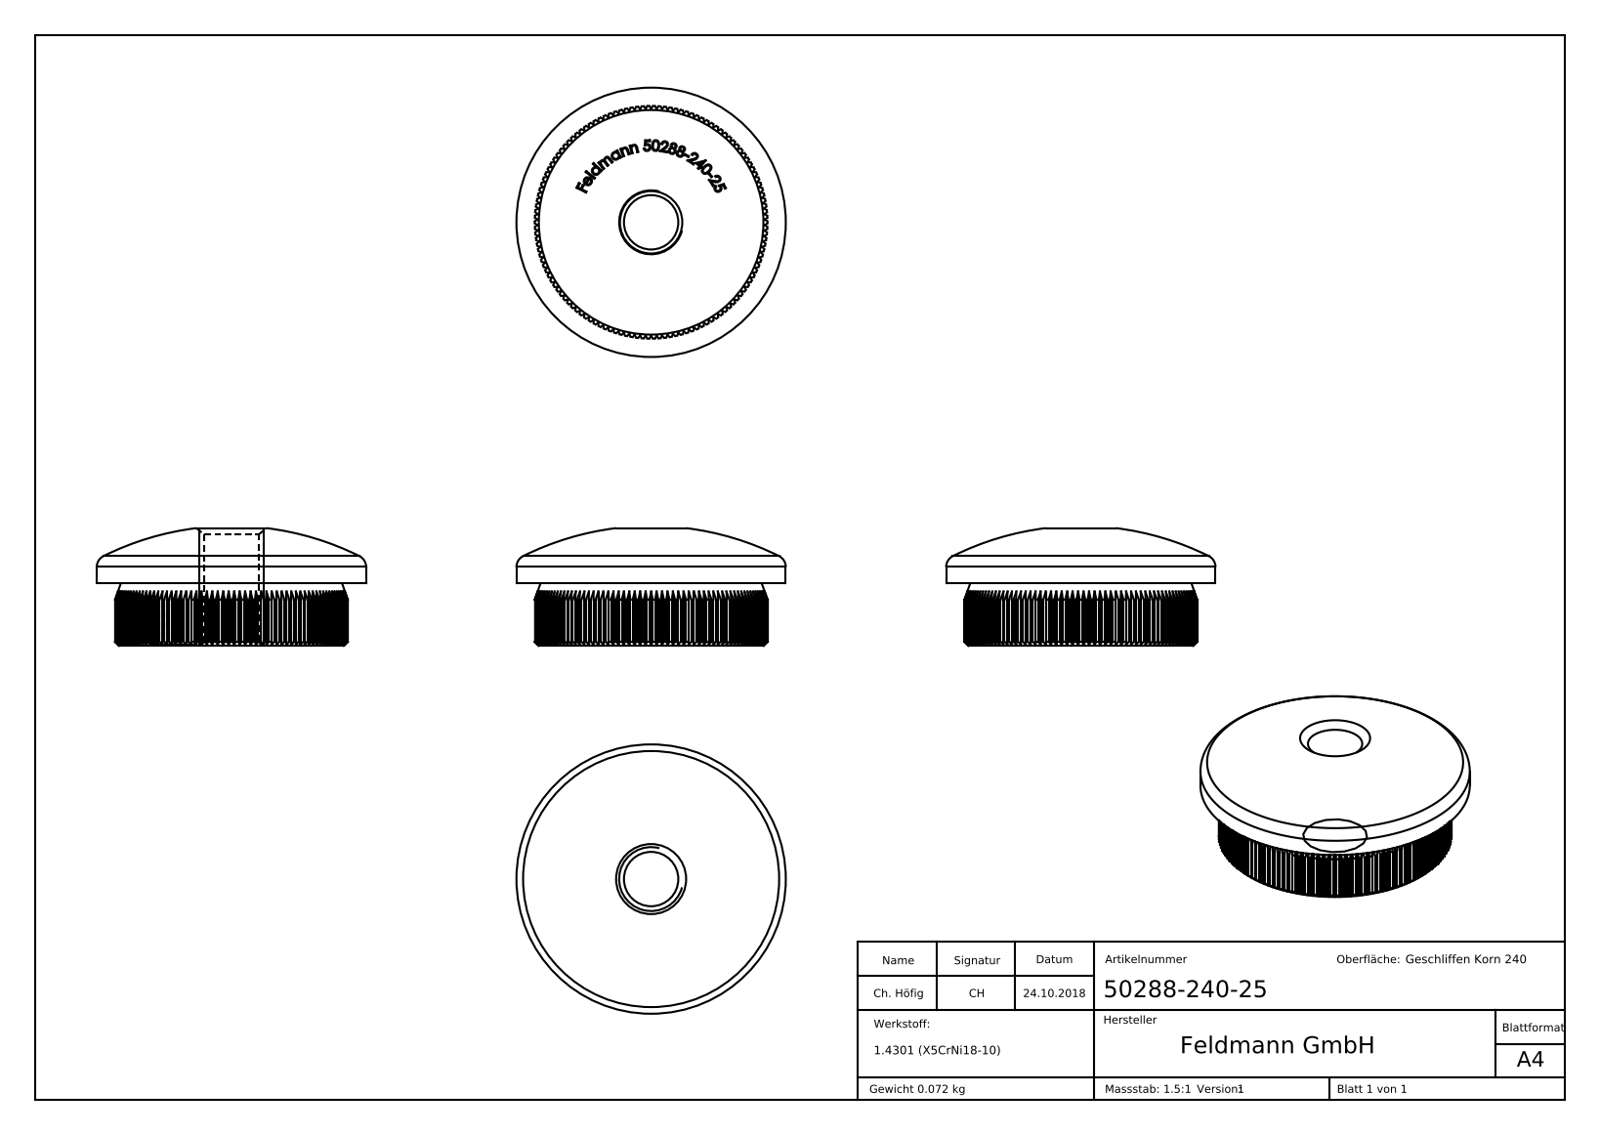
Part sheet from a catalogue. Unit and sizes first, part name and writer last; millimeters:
Units: millimetres
Overall size (bounding box): 33.7 × 33.7 × 14.73
Round holes (diameter × count): ⌀6.8 ×1
Round bosses / shafts (diameter × count): ⌀33.7 ×1
Partial cylindrical surfaces — rounded edges, fillets, slot ends (radius × count): R14.55 ×1
Main face-to-face distances: 7.8, 14.2, 14.22, 14.18, 7.7, 0.66, 0.54, 7.4, 6.8, 0.67
Volume: 9 078 mm³ · Surface area: 3 434 mm²
Bodies: 1 solid, 633 faces (392 planar, 134 cylindrical, 107 other)
Part name (STEP PRODUCT): 50288-240-25
STEP written by: SolidWorks 2015 (CONFIG_CONTROL_DESIGN)
